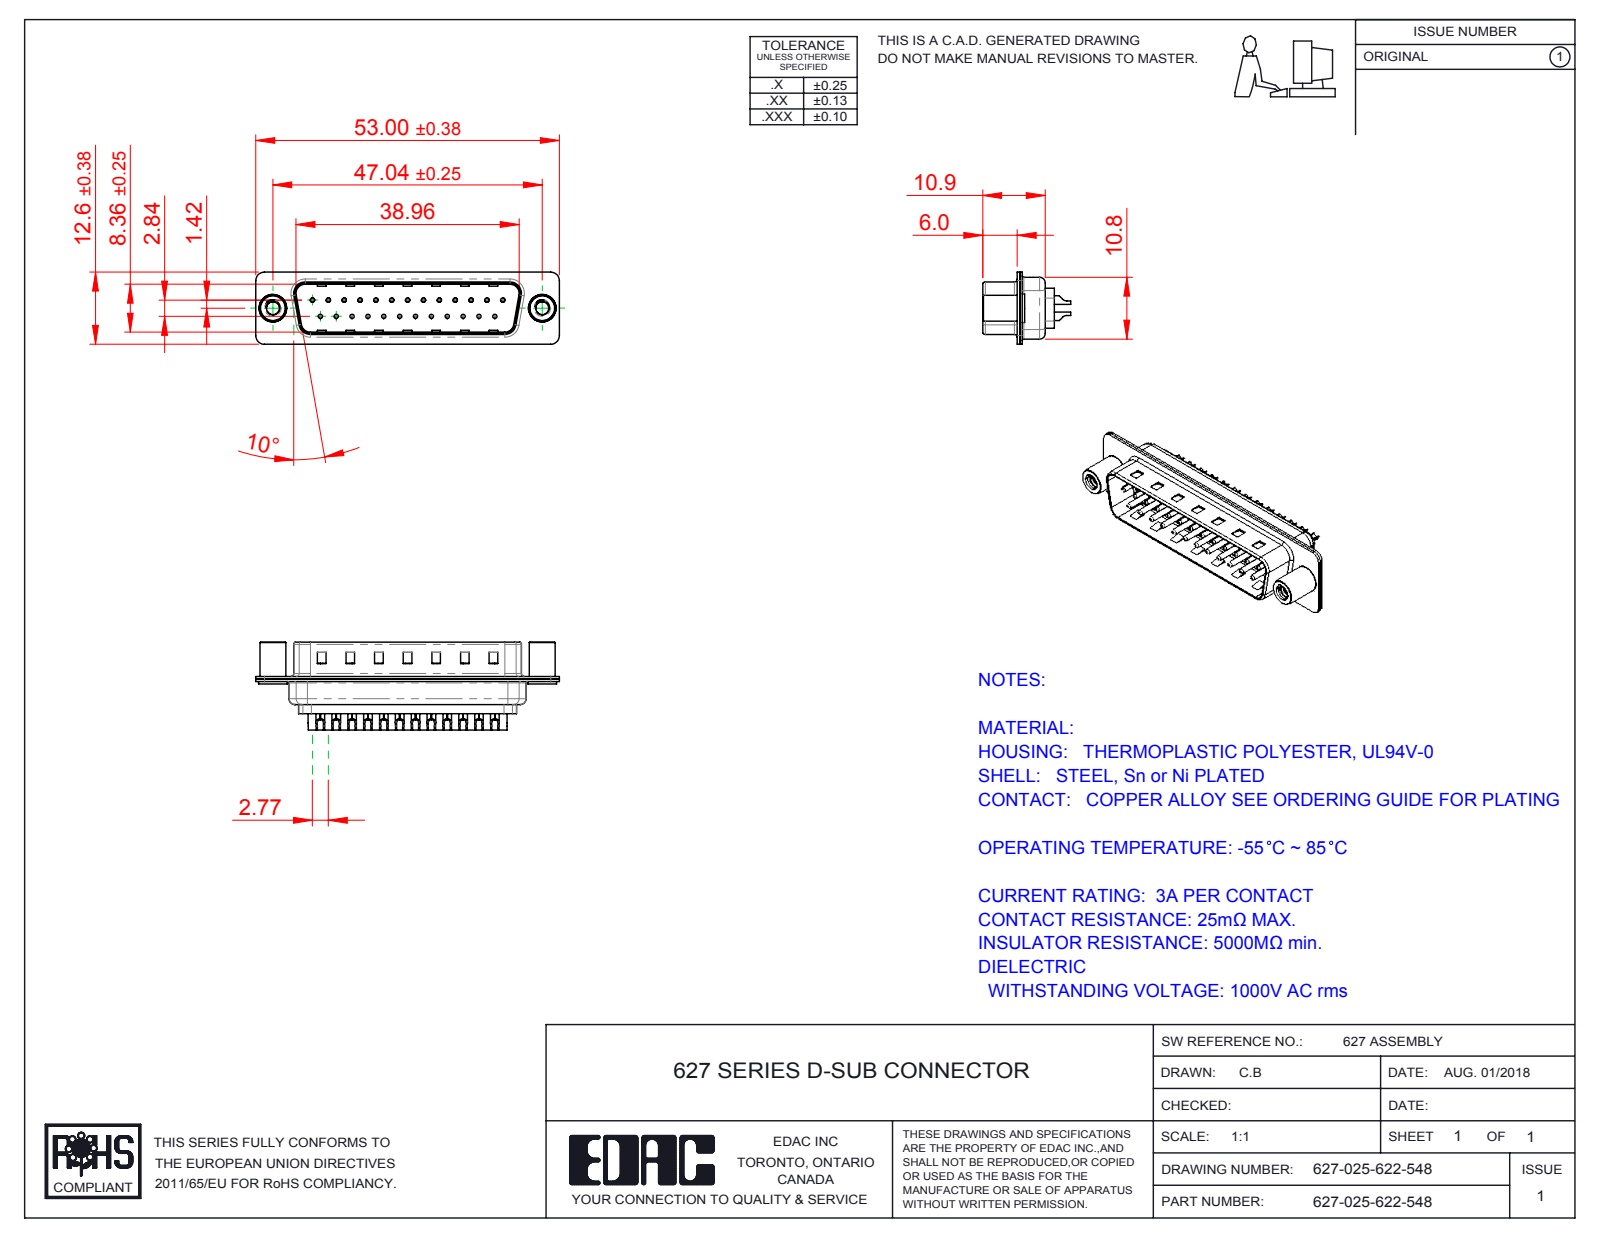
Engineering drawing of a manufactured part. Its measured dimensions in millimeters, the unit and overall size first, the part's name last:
Units: millimetres
Overall size (bounding box): 53 × 15.35 × 12.6
Round holes (diameter × count): ⌀0.35 ×25, ⌀1.1 ×25, ⌀1.6 ×25, ⌀2.26 ×2, ⌀4 ×2, ⌀4.8 ×2
Round bosses / shafts (diameter × count): ⌀2 ×25, ⌀1.5 ×25, ⌀0.75 ×25, ⌀5 ×2, ⌀4.9 ×2, ⌀4.5 ×2
Partial cylindrical surfaces — rounded edges, fillets, slot ends (radius × count): R1.5 ×16, R2 ×12, R0.5 ×8, R1.6 ×8, R1 ×6, R0.25 ×4, R0.6 ×4, R0.65 ×4
Main face-to-face distances: 0.4, 0.45, 0.82, 9.58, 0.9, 8.76, 1.5, 1.4, 6.5, 6.05
Hole centre spacings: 3.16, 8.31, 2.77, 5.54, 11.08, 16.62, 5.03, 5.04
Volume: 2 755 mm³ · Surface area: 8 056 mm²
Bodies: 30 solids, 2010 faces (523 planar, 890 cylindrical, 597 other)
Part name (STEP PRODUCT): 627 4-40 Threaded Standoff; 627 Shell Rear_25 Contacts; 627 Shell Front_25 Contacts; 627 Contact Row 2_22L (+3 more)
STEP written by: SolidWorks 2016 (CONFIG_CONTROL_DESIGN)
